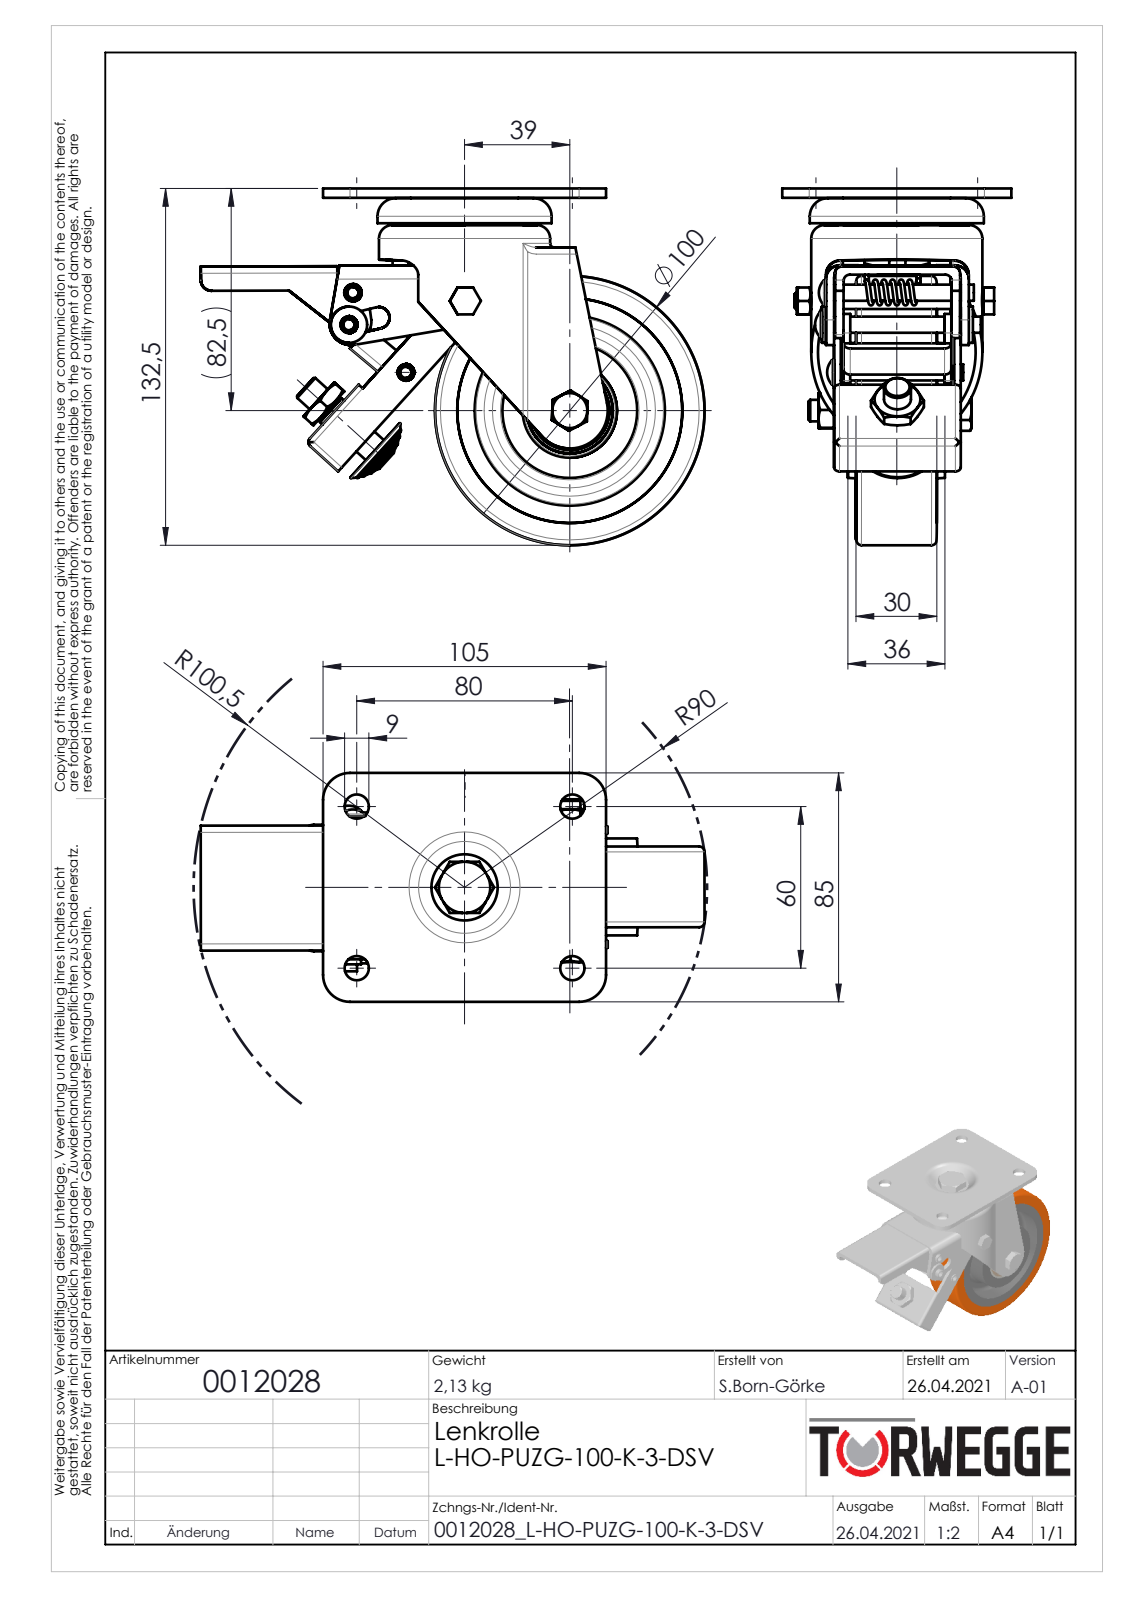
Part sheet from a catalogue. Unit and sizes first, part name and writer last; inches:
Units: inches
Overall size (bounding box): 7.359 × 5.215 × 3.346
Round holes (diameter × count): ⌀0.354 ×4, ⌀0.163 ×3, ⌀0.248 ×3, ⌀0.252 ×3, ⌀0.236 ×1, ⌀0.244 ×1, ⌀0.256 ×1, ⌀0.315 ×1, ⌀0.323 ×1, ⌀0.33 ×1, ⌀0.335 ×1, ⌀0.551 ×1
Round bosses / shafts (diameter × count): ⌀0.236 ×5, ⌀0.374 ×3, ⌀0.787 ×2, ⌀0.531 ×2, ⌀3.937 ×1, ⌀2.5 ×1, ⌀2.173 ×1, ⌀2.127 ×1
Partial cylindrical surfaces — rounded edges, fillets, slot ends (radius × count): R0.157 ×8, R0.098 ×6, R0.079 ×5, R0.126 ×4, R0.236 ×4, R0.394 ×4, R0.089 ×2, R0.101 ×2
Main face-to-face distances: 0.137, 0.118, 0.098, 1.181, 0.098, 0.047, 0.193, 0.13, 1.839, 1.299
Hole centre spacings: 0.471, 1.398, 1.969, 3.606, 1.085, 1.357, 1.358, 1.646
Bodies: 0 solids, 865 faces (241 planar, 231 cylindrical, 393 other)
Part name (STEP PRODUCT): 0012028
STEP written by: SolidWorks 2020 (AUTOMOTIVE_DESIGN)
